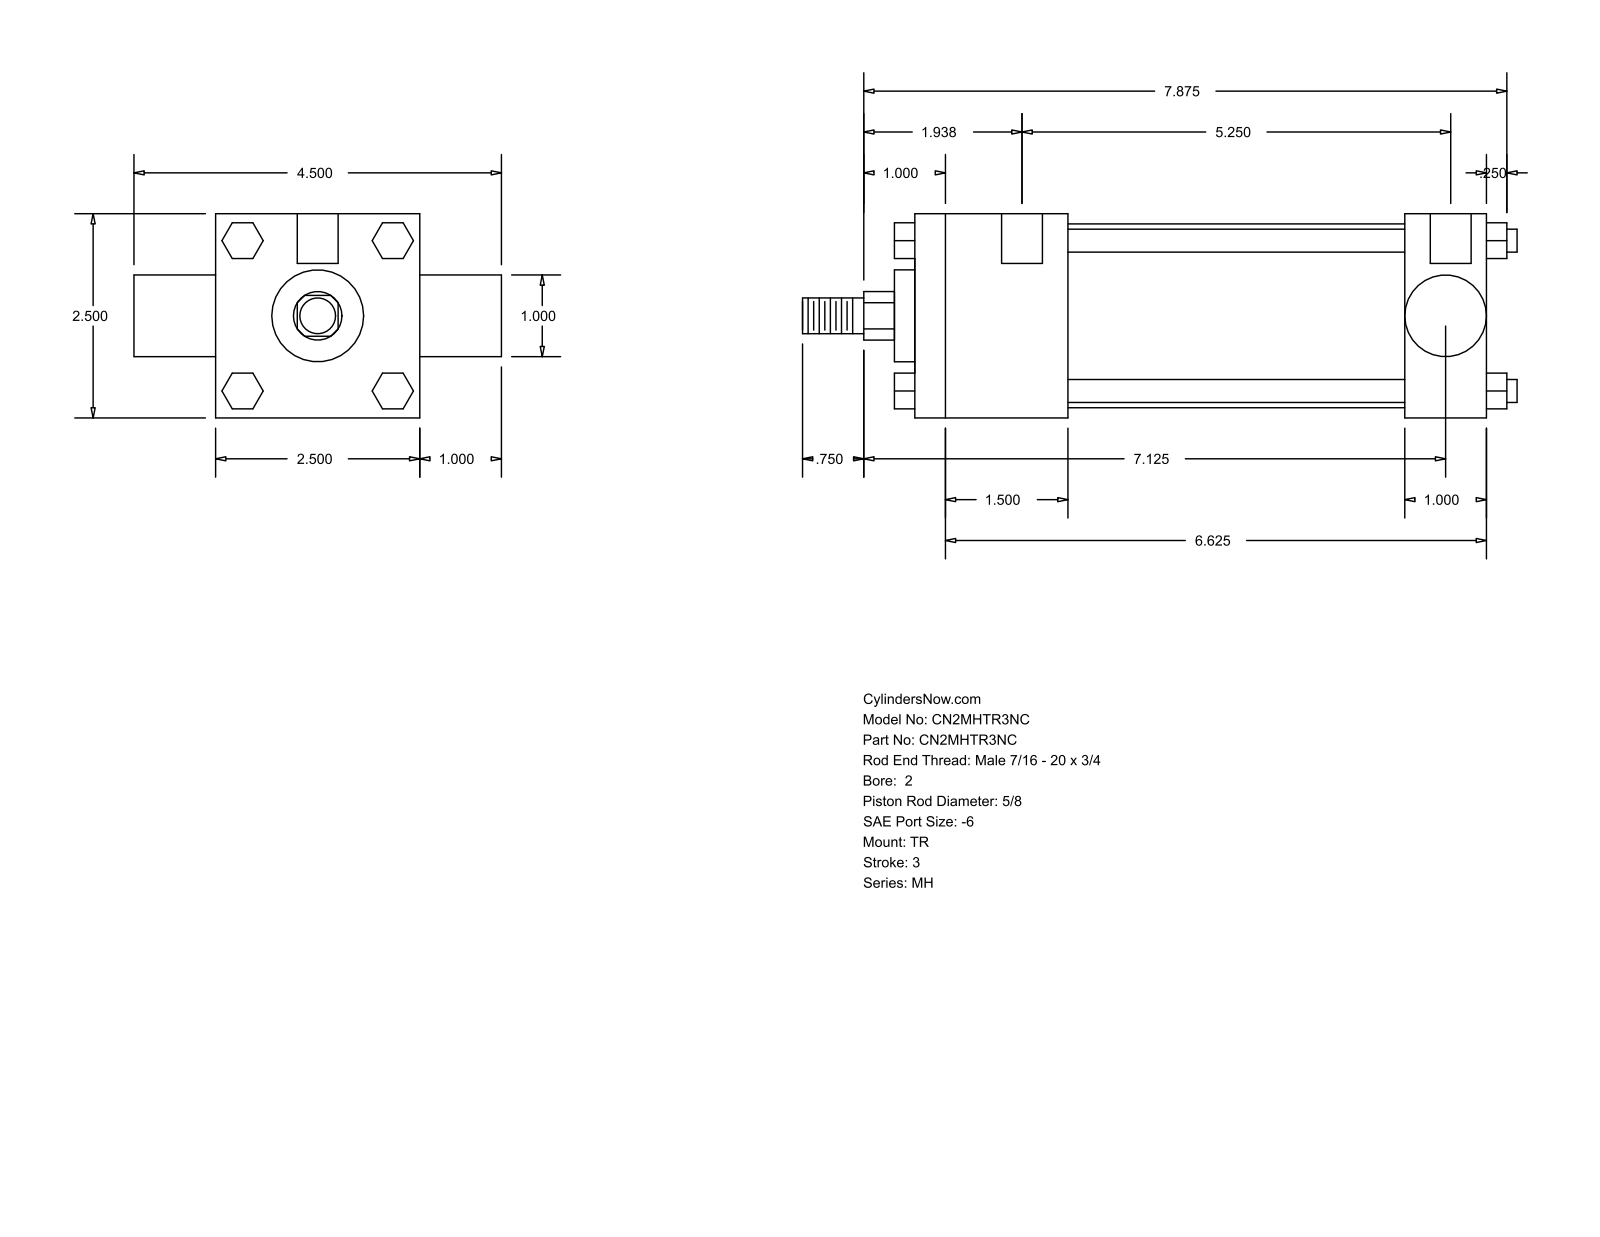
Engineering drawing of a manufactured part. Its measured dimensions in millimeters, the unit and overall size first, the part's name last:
Units: millimetres
Overall size (bounding box): 222.25 × 114.3 × 63.5
Round holes (diameter × count): ⌀5.56 ×3, ⌀12.7 ×2
Round bosses / shafts (diameter × count): ⌀7.14 ×4, ⌀57.15 ×1, ⌀28.57 ×1, ⌀25.35 ×1, ⌀15.88 ×1, ⌀11.11 ×1
Partial cylindrical surfaces — rounded edges, fillets, slot ends (radius × count): R7.54 ×1
Main face-to-face distances: 63.5, 177.8, 25.4, 47.62, 152.4, 104.78, 130.18, 6.35, 88.9, 184.15
Hole centre spacings: 3.18, 4.76, 133.35, 136.53, 138.11, 141.29
Bodies: 0 solids, 120 faces (92 planar, 28 cylindrical, 0 other)
Part name (STEP PRODUCT): MH_TR__0200_0.625
STEP written by: GSSL Pune (CONFIG_CONTROL_DESIGN)
